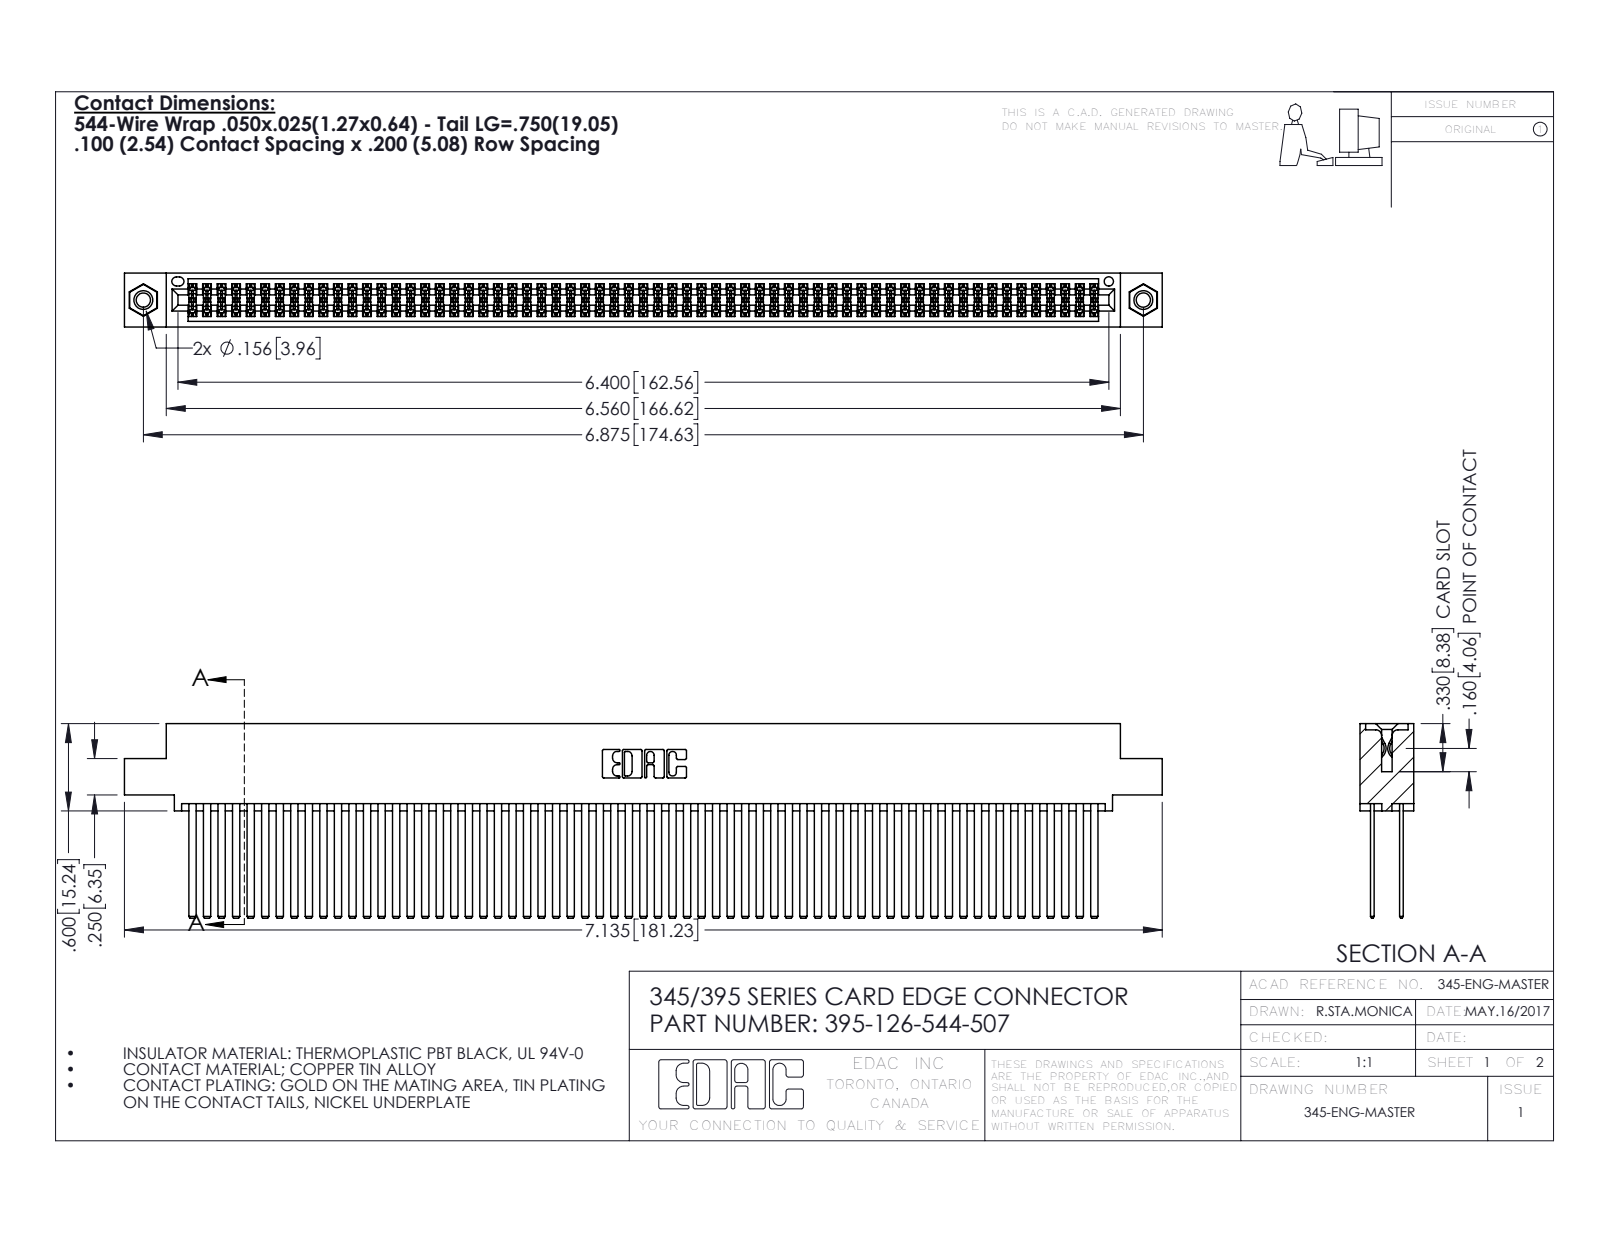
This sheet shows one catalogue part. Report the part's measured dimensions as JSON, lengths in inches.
{"part_name": "345-250-001_345-250-005-103; 395-126-544-507; 345-292-001_345-293-144; 345 Part_0.110 Offset - 0.156 Dia-TI", "step_written_by": "SolidWorks 2016 (CONFIG_CONTROL_DESIGN)", "units": "inches", "bodies": {"solids": 129, "faces": 5734, "planar": 3770, "cylindrical": 1948, "other": 16}, "overall_size": [7.135, 1.337, 0.37], "volume_in3": 1.189, "surface_area_in2": 53.47, "round_holes": [[0.098, 2], [0.125, 2], [0.156, 2], [0.064, 1]], "round_bosses_or_shafts": [[0.155, 2]], "partial_cylinders_radius": [[0.006, 189], [0.01, 22], [0.007, 6], [0.031, 6], [0.026, 3], [0.014, 2], [0.019, 2], [0.022, 2]], "face_to_face_distances": [0.2, 0.025, 0.072, 0.098, 0.272, 0.298, 0.225, 0.175, 0.37, 0.149], "hole_center_spacings": [0.27, 6.639, 6.875]}
